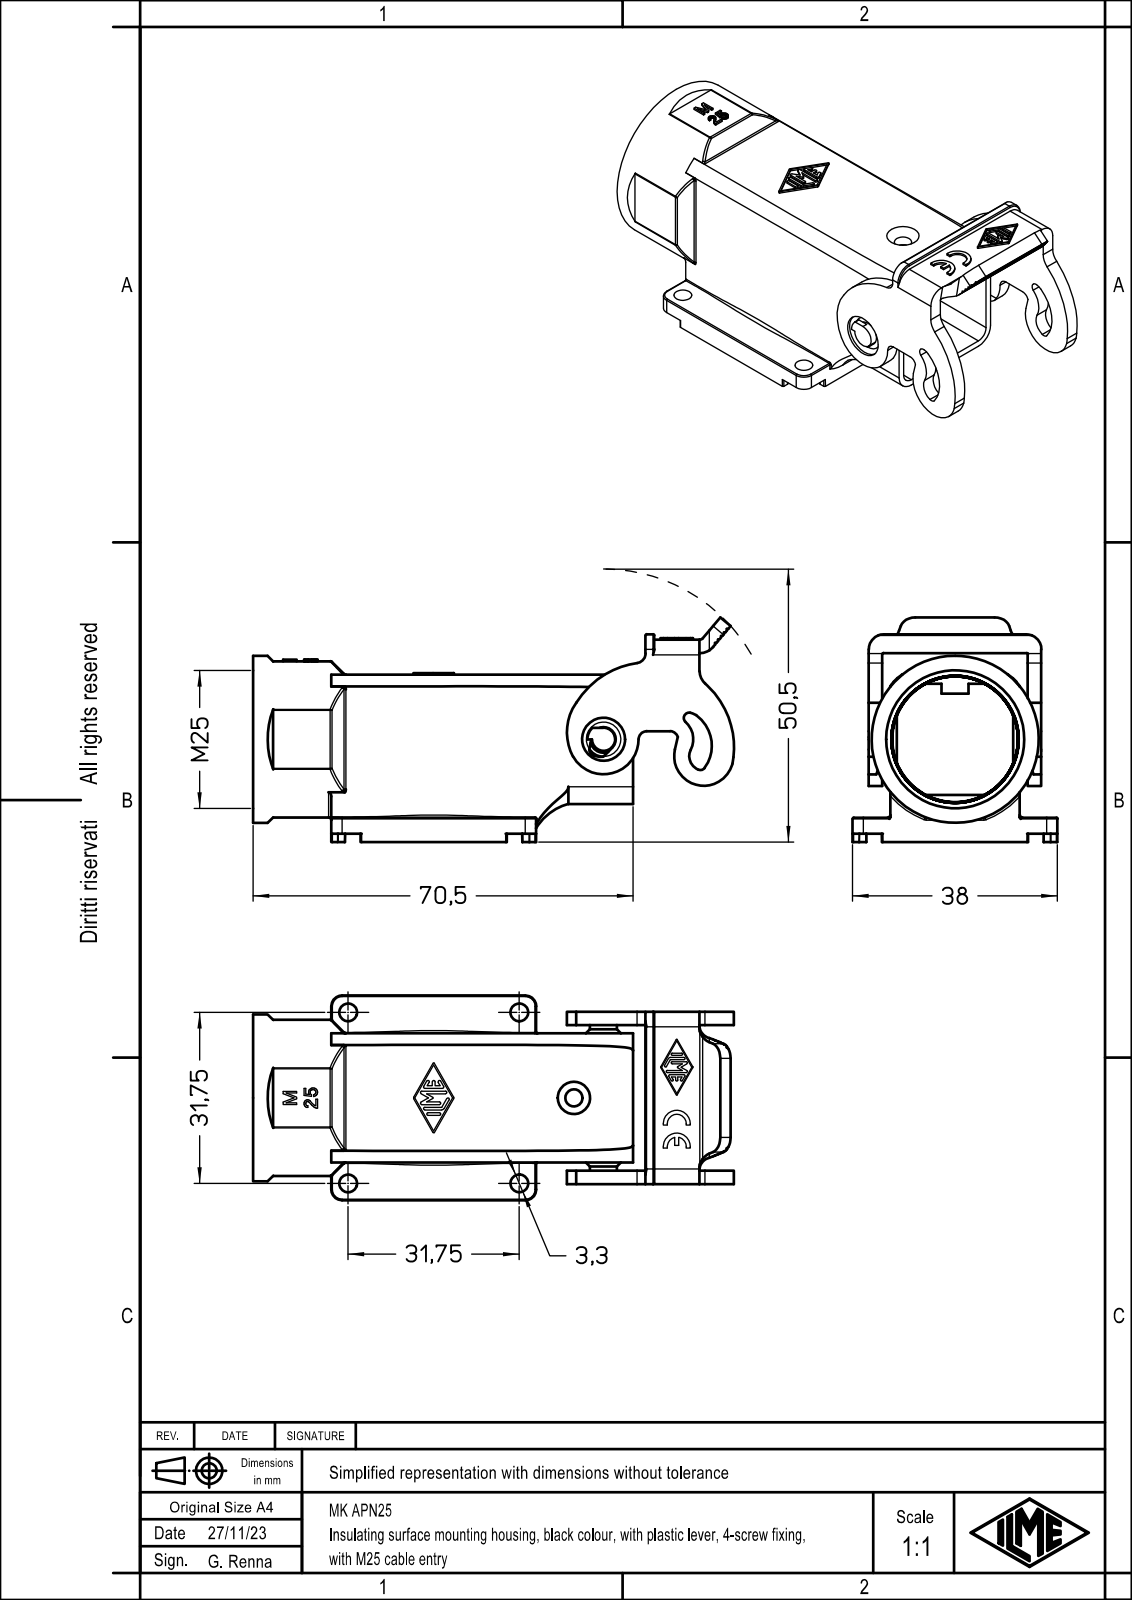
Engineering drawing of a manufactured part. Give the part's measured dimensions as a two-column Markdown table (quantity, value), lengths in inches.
| quantity | value |
| --- | --- |
| part name | MK APN25 |
| STEP written by | Creo Elements/Direct Modeling 20.1B 02-Apr-2019 (C) Parametric Technology GmbH (AUTOMOTIVE_DESIGN) |
| units | inches |
| bodies | 1 solid, 644 faces (334 planar, 207 cylindrical, 103 other) |
| overall size | 3.512 × 1.641 × 1.496 |
| volume | 1.188 in³ |
| surface area | 30.36 in² |
| round holes (diameter × count) | 0.13 × 4, 0.126 × 1, 0.315 × 1, 0.929 × 1 |
| round bosses / shafts (diameter × count) | 1.22 × 1, 0.197 × 1, 0.169 × 1 |
| partial cylindrical surfaces (radius × count) | 0.008 × 51, 0.02 × 16, 0.079 × 16, 0.01 × 15, 0.004 × 7, 0.126 × 7, 0.11 × 6, 0.012 × 4 |
| main face-to-face distances | 0.047, 0.898, 0.098, 0.945, 1.102, 1.161, 0.157, 0.059, 0.85, 1.055 |
| hole center spacings | 1.25, 1.763, 1.768, 0.741, 0.741 |
